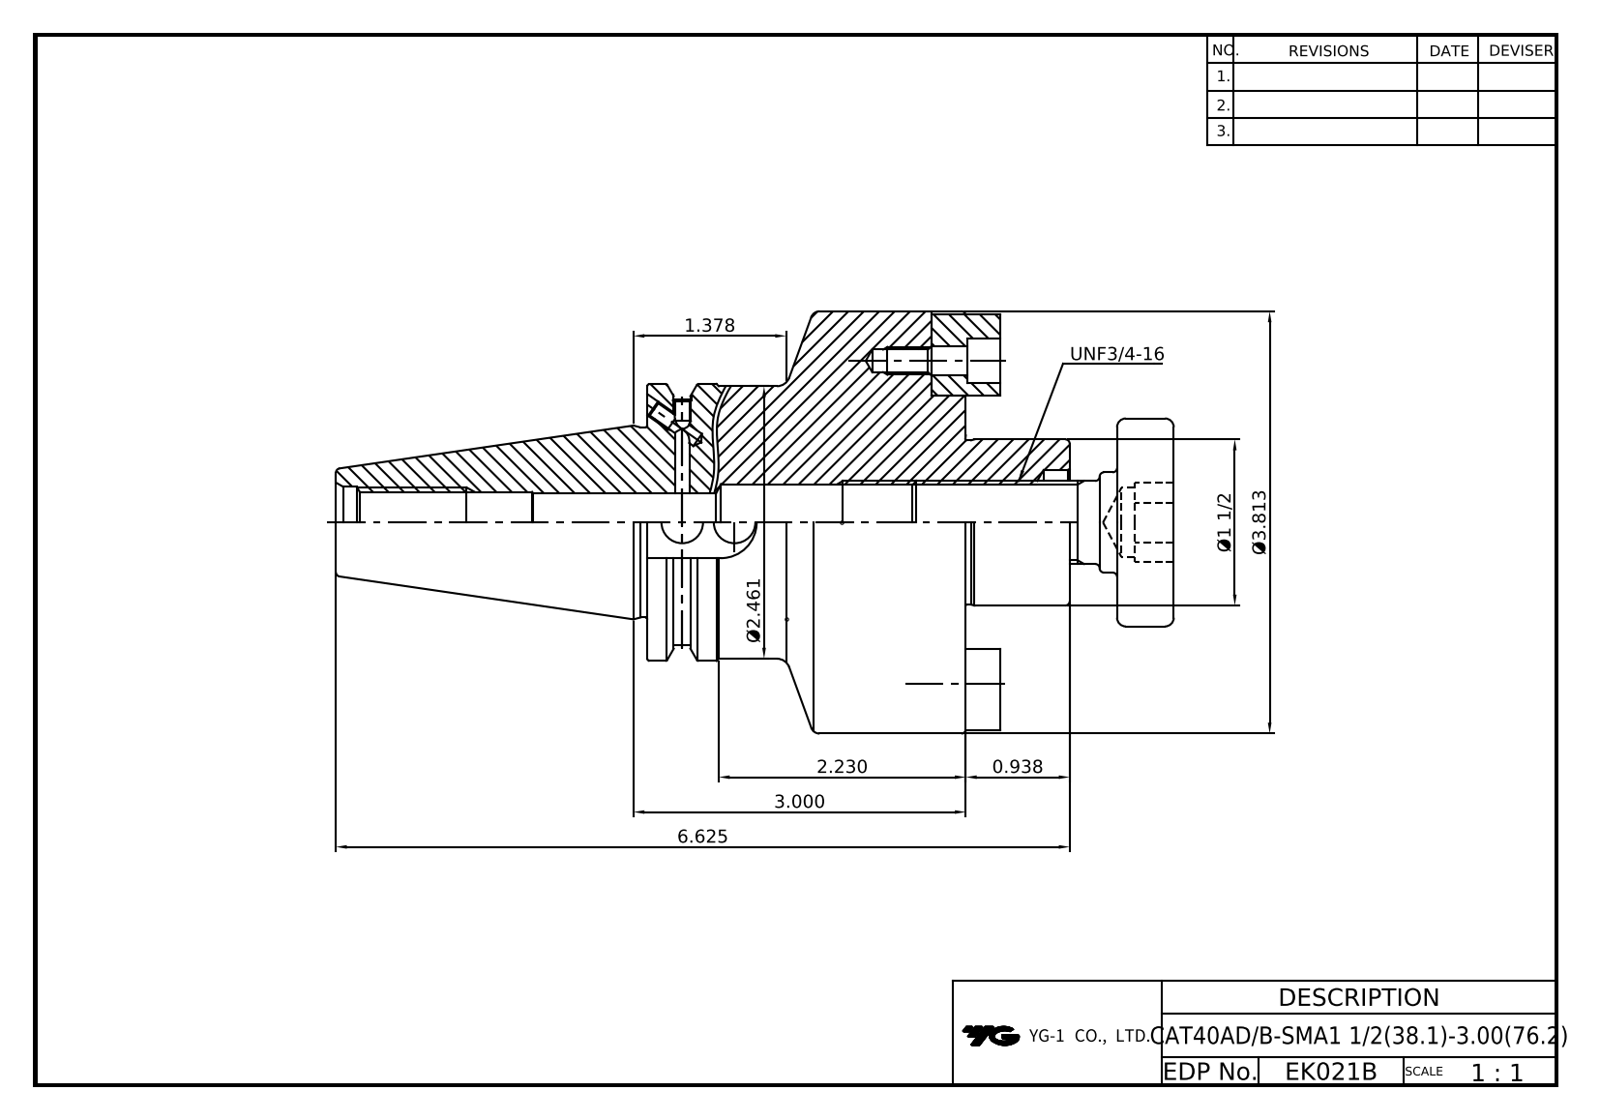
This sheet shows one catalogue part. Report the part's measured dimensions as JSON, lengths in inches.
{"part_name": "LO-CAT40ADB-SMA38.1-76.2; HEX'' WRENCH BOLT-UNC1_4-20x5_8L; DRIVE KEY-15.875x15.875x18.5; COLLAR BOLT-UNF3_4-16x47L", "step_written_by": "Autodesk Inventor 2022 (AUTOMOTIVE_DESIGN)", "units": "inches", "bodies": {"solids": 6, "faces": 176, "planar": 83, "cylindrical": 50, "other": 43}, "overall_size": [7.925, 3.813, 3.813], "volume_in3": 29.37, "surface_area_in2": 102.2, "round_holes": [[0.128, 4], [0.157, 2], [0.165, 2], [0.196, 2], [0.26, 2], [0.406, 2], [0.375, 1], [0.512, 1], [0.527, 1], [0.625, 1], [0.642, 1], [0.682, 1]], "round_bosses_or_shafts": [[0.375, 2], [0.25, 2], [3.813, 1], [2.5, 1], [2.461, 1], [1.878, 1], [1.717, 1], [1.5, 1]], "partial_cylinders_radius": [[0.312, 2], [0.322, 1], [1.108, 1]], "face_to_face_distances": [2.237, 2.875, 5.113, 4.601, 1.726, 0.512, 2.562, 0.313, 2.039, 2.55], "hole_center_spacings": [1.459, 2.918]}
